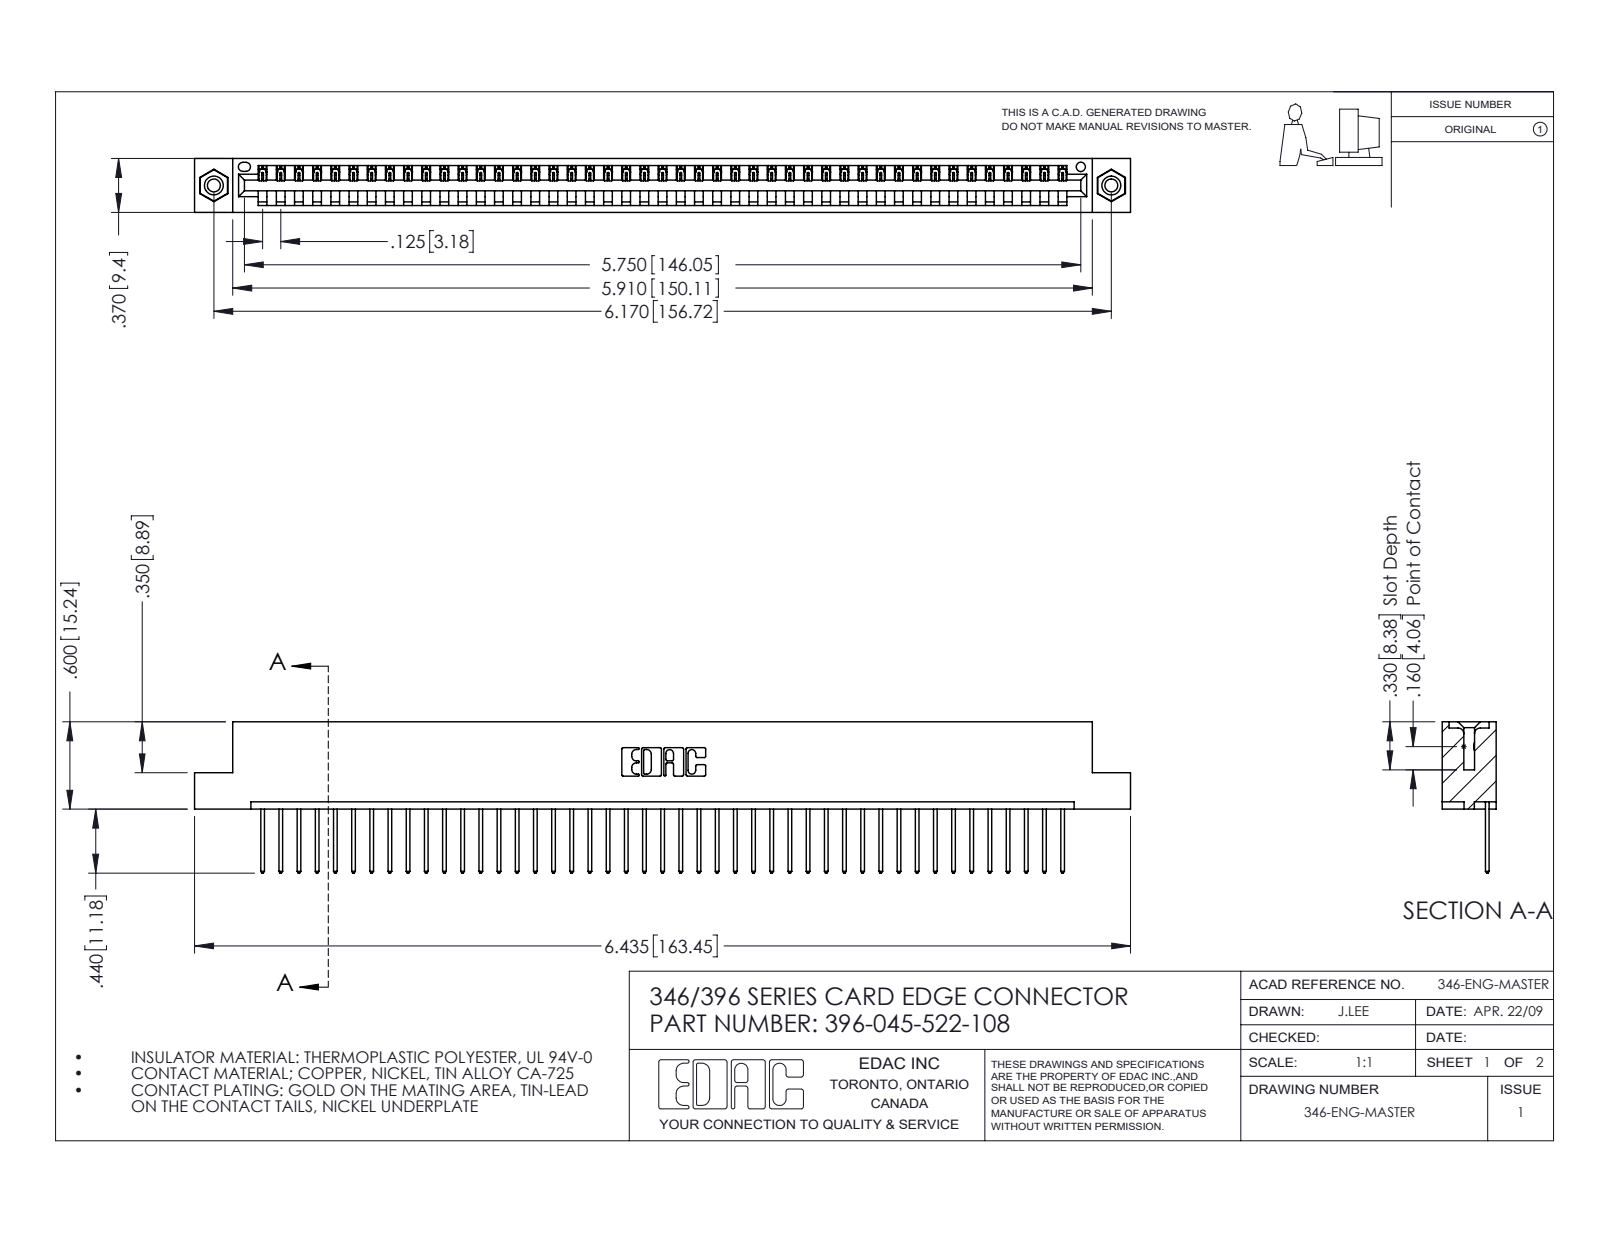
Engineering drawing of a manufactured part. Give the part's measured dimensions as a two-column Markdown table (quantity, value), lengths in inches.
| quantity | value |
| --- | --- |
| part name | 346 Part_Flush Mounting Lugs - 0.156 Dia-TI; 396-045-522-108; 345-250-001_345-250-003-102; 345-292-001_345-293-122 |
| STEP written by | SolidWorks 2016 (CONFIG_CONTROL_DESIGN) |
| units | inches |
| bodies | 48 solids, 2792 faces (1908 planar, 868 cylindrical, 16 other) |
| overall size | 6.435 × 1.04 × 0.37 |
| volume | 0.956 in³ |
| surface area | 30.69 in² |
| round holes (diameter × count) | 0.089 × 2, 0.125 × 2, 0.156 × 2, 0.064 × 1 |
| round bosses / shafts (diameter × count) | 0.155 × 2 |
| partial cylindrical surfaces (radius × count) | 0.006 × 90, 0.01 × 90, 0.01 × 22, 0.007 × 6, 0.031 × 6, 0.026 × 3, 0.031 × 2, 0.04 × 2 |
| main face-to-face distances | 0.048, 0.322, 0.37, 0.25, 0.072, 0.298, 0.025, 0.148, 0.222, 0.1 |
| hole center spacings | 0.246, 5.961, 6.17 |
